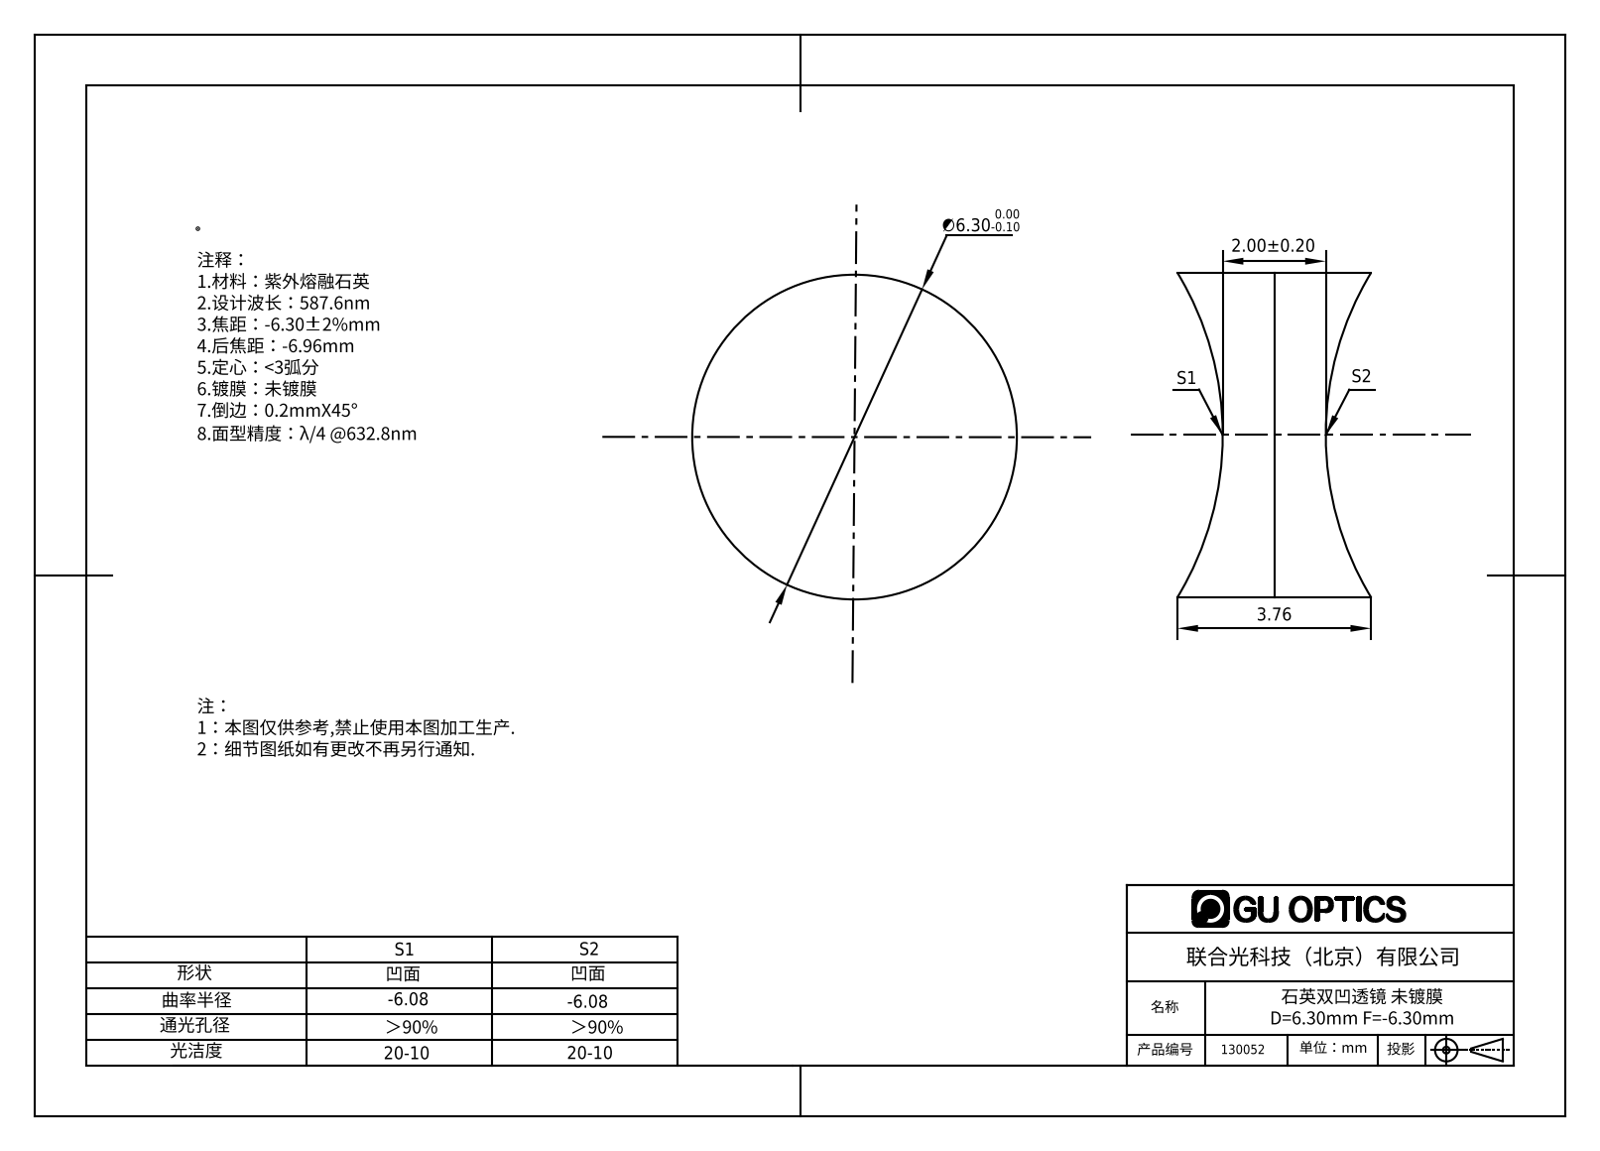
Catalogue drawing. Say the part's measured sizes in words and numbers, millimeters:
The part is named "130052". Its 3-D file was written by "SolidWorks 2016 (AUTOMOTIVE_DESIGN)". It is 1 solid with 6 faces: 0 planar, 2 cylindrical and 4 other. Overall it measures 6.3 by 6.3 by 3.76 millimeters. Its volume is 89 cubic millimeters and its surface area 142 square millimeters. Round bosses or shafts: 1 of diameter 6.3.
